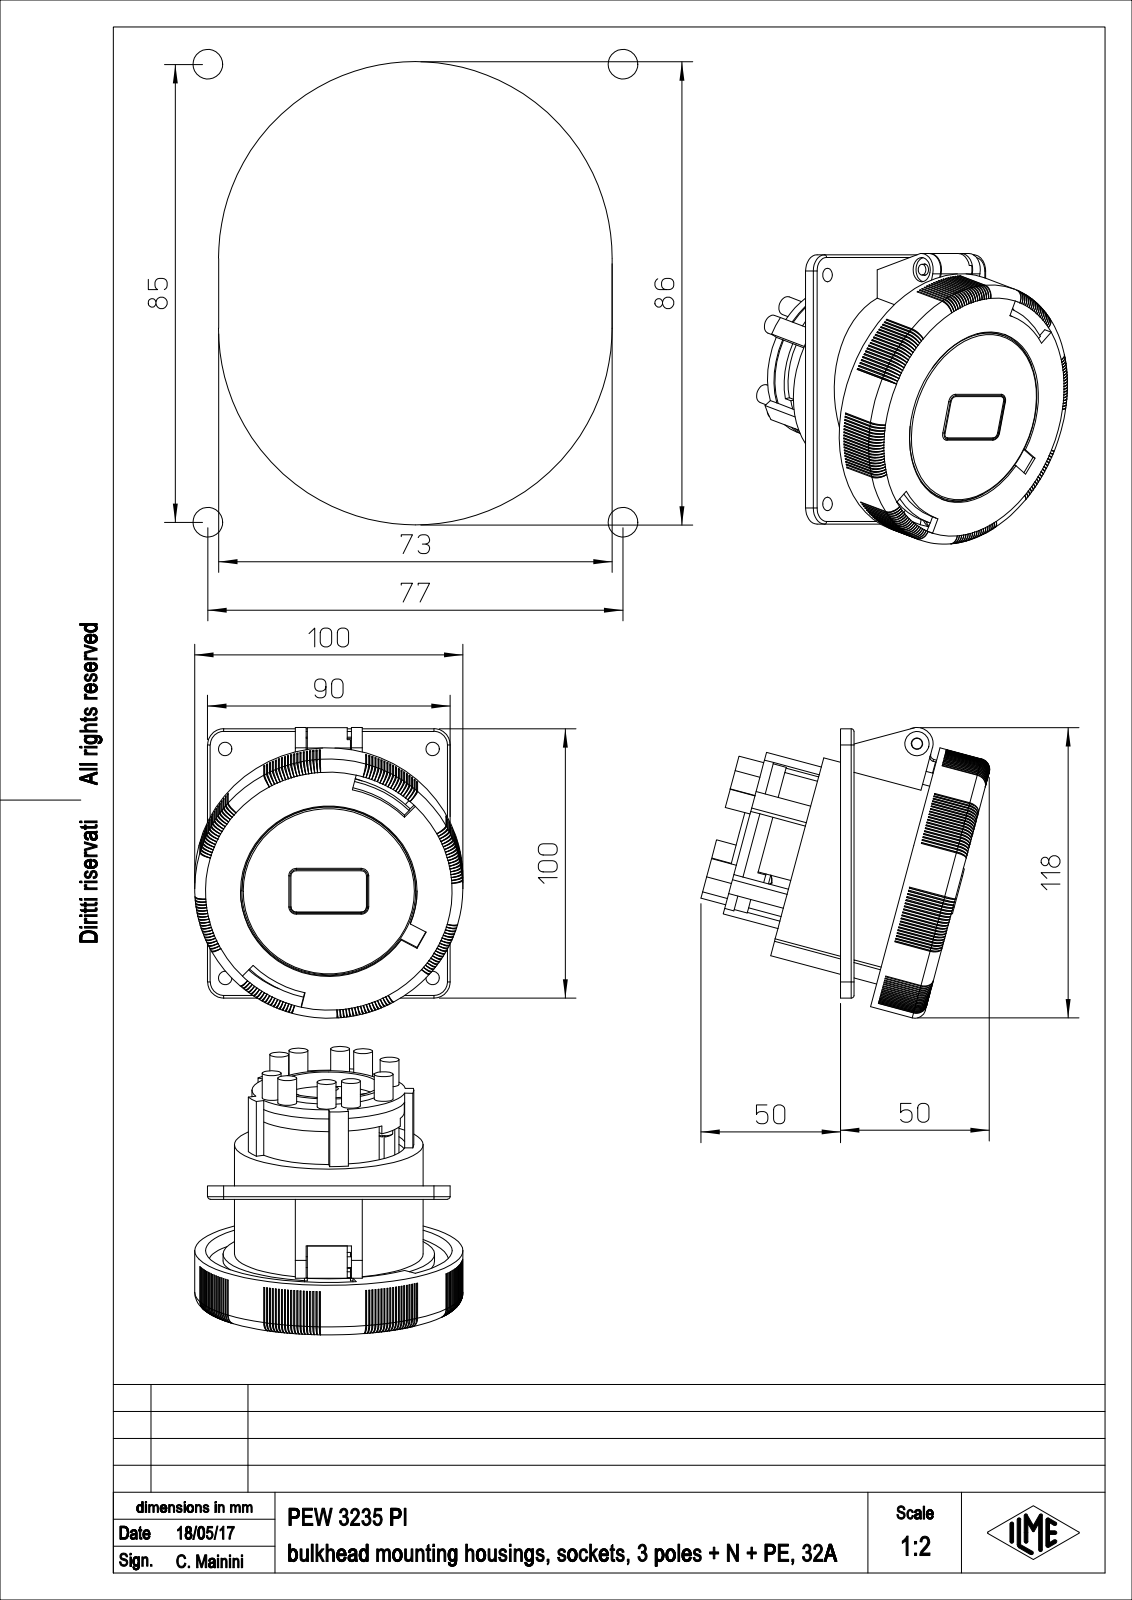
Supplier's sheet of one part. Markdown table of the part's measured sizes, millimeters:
| quantity | value |
| --- | --- |
| part name | PEW_3235_PI |
| STEP written by | PTC Creo Elements/Direct Modeling 19.0E 27-Jun-2016 (C) Parametric Technology GmbH (AUTOMOTIVE_DESIGN) |
| units | millimeters |
| bodies | 1 solid, 1440 faces (642 planar, 307 cylindrical, 491 other) |
| overall size | 107.91 × 107.09 × 99.5 |
| volume | 269 783 mm³ |
| surface area | 105 069 mm² |
| round holes (diameter × count) | 7 × 5, 5 × 4, 7.5 × 4, 14 × 4, 4.2 × 1, 9 × 1, 9.5 × 1, 37 × 1, 57 × 1, 58.5 × 1, 61.7 × 1, 65.3 × 1 |
| round bosses / shafts (diameter × count) | 7 × 11, 6.7 × 2, 99.5 × 1, 85 × 1, 78.5 × 1, 75.5 × 1, 70 × 1, 64.5 × 1 |
| partial cylindrical surfaces (radius × count) | 3.6 × 152, 6 × 6, 0.4 × 4, 1 × 4, 2 × 4, 0.2 × 3, 4 × 2, 26 × 2 |
| main face-to-face distances | 5, 3, 57.7, 2, 20, 17, 60.7, 40.7, 6.7, 11.19 |
| hole center spacings | 28.81, 17.81, 15.15, 15.14, 15.16, 28.82, 17.8, 15.12 |
